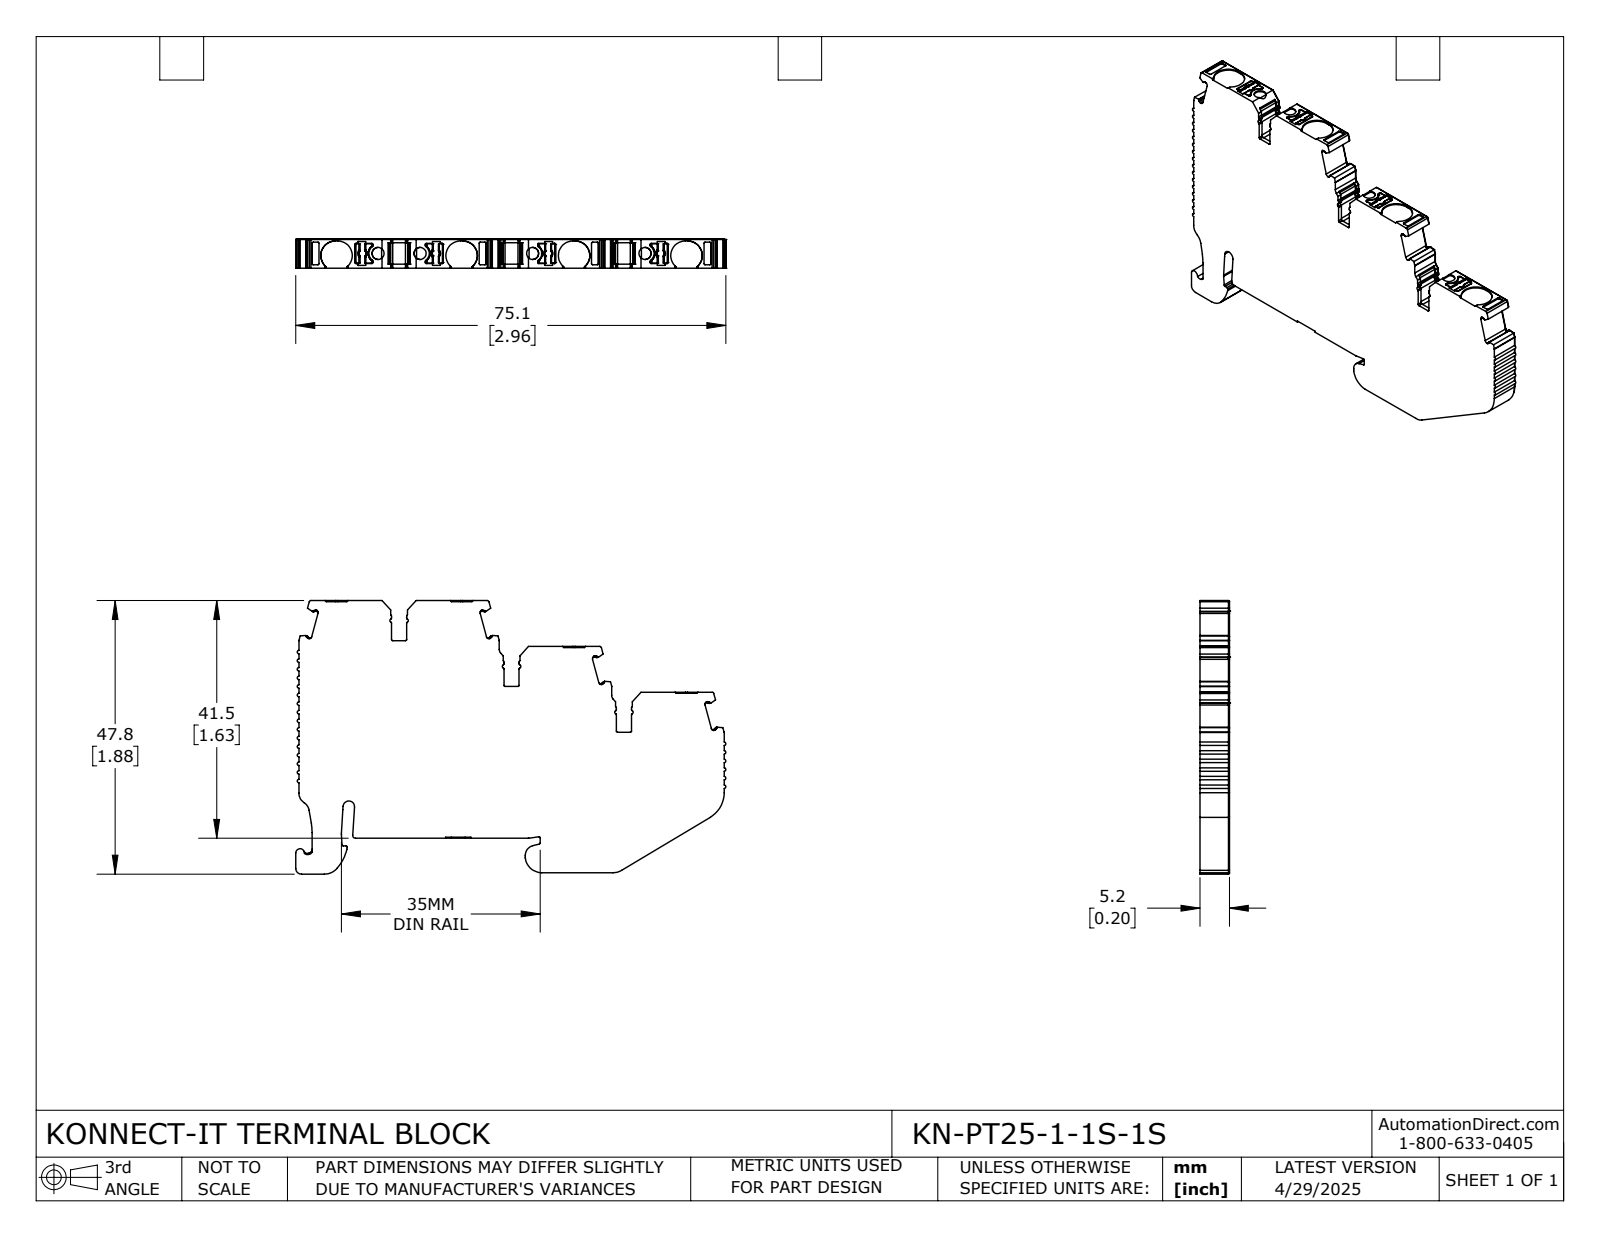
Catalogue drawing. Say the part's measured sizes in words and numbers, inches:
The part is named "KN-PT25-1-1S-1S". Its 3-D file was written by "SolidWorks 2024 (CONFIG_CONTROL_DESIGN)". It is 1 solid with 936 faces: 442 planar, 423 cylindrical and 71 other. Overall it measures 2.957 by 1.88 by 0.203 inches. Its volume is 0.813 cubic inches and its surface area 10.75 square inches. Round holes: 4 of diameter 0.083. Partial cylindrical surfaces (rounded edges, fillets, slot ends): 92 of radius 0.008, 59 of radius 0.012, 35 of radius 0.004, 16 of radius 0.006, 16 of radius 0.02, 13 of radius 0.016, 8 of radius 0.006, 8 of radius 0.01. The main face-to-face distances are 0.203, 0.315, 0.63, 0.236, 0.63, 0.315, 0.307, 0.323, 0.079, 0.773. The hole center spacings are 0.289, 0.773, 0.773, 1.062, 1.546, 1.835.
